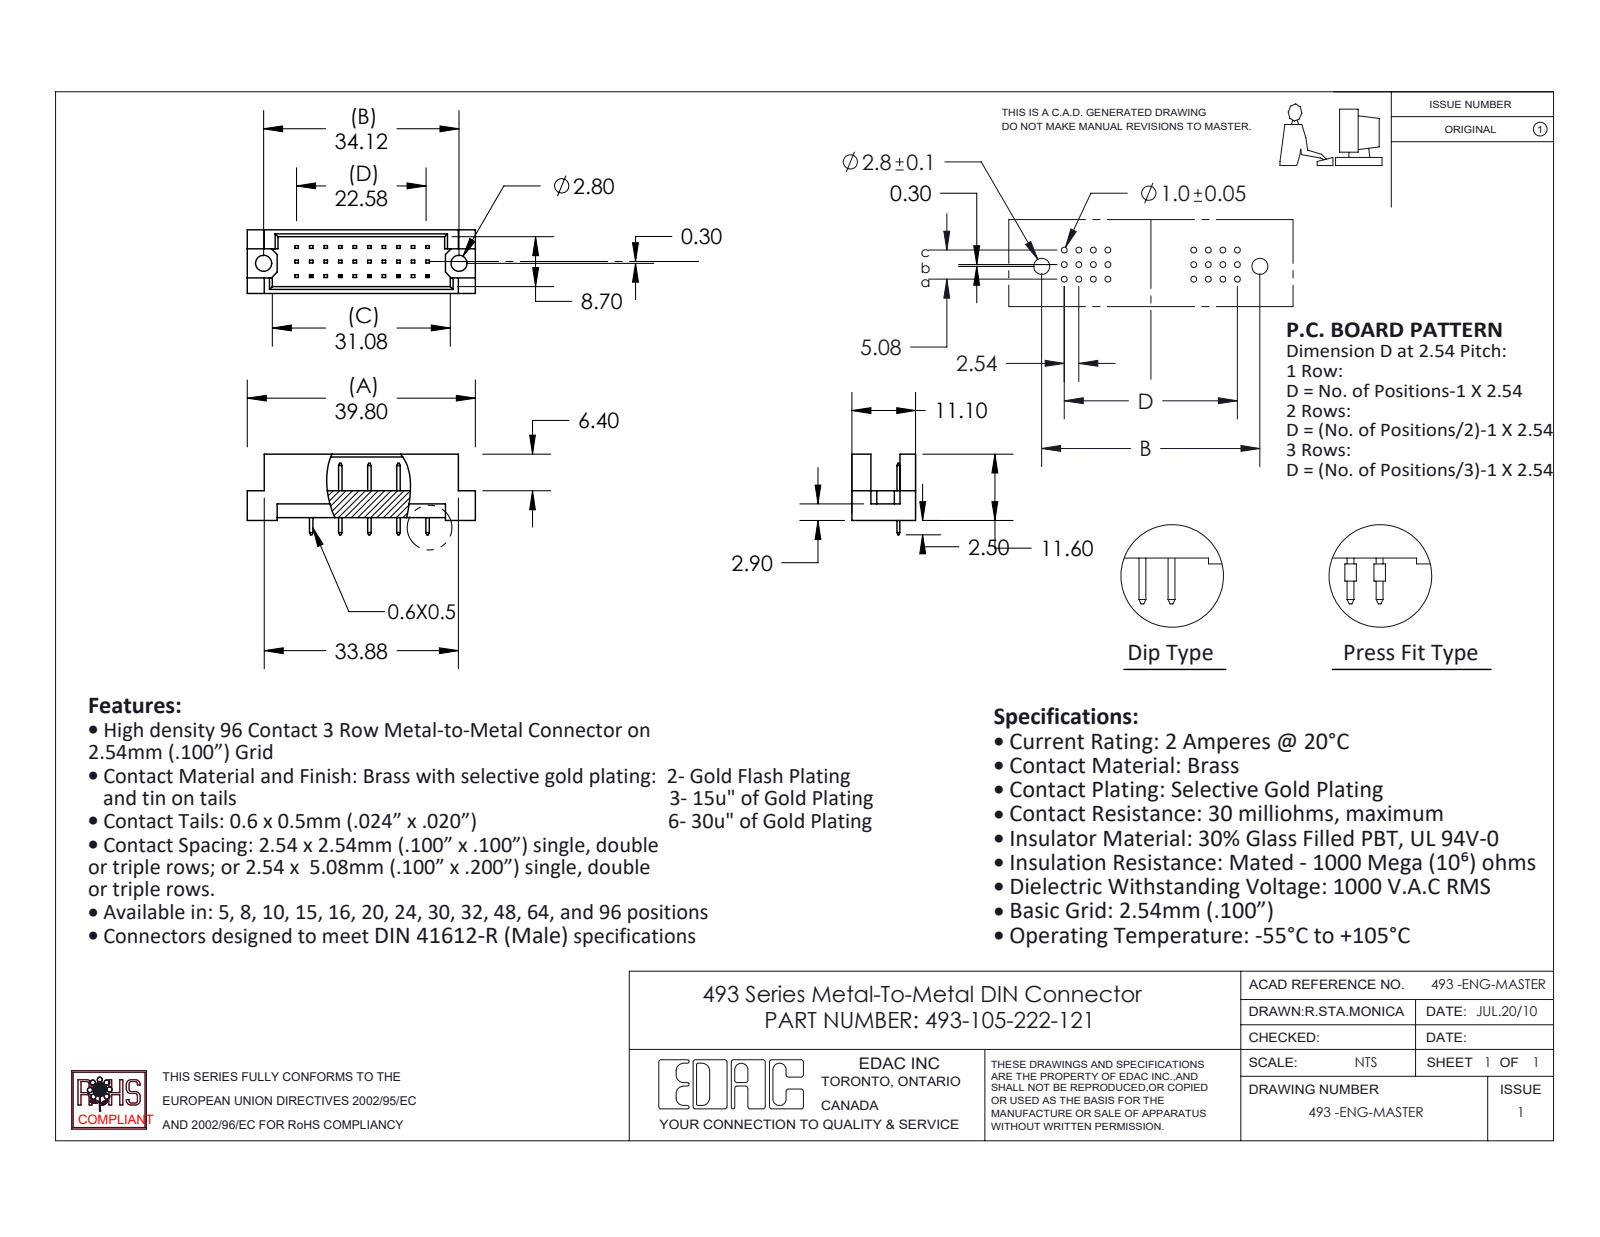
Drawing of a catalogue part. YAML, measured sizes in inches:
part_name: "493-105-222-121; 493 Part_30; 493-290_22"
step_written_by: "SolidWorks 2020 (CONFIG_CONTROL_DESIGN)"
units: inches
bodies: {solids: 6, faces: 242, planar: 238, cylindrical: 4, other: 0}
overall_size: [1.567, 0.555, 0.437]
volume: 0.146
surface_area: 4.453
round_holes:
  - {diameter: 0.11, count: 2}
face_to_face_distances: [0.047, 0.39, 0.437, 0.343, 0.185, 0.02, 0.2, 0.094, 0.1, 0.091]
hole_center_spacings: [1.343]
